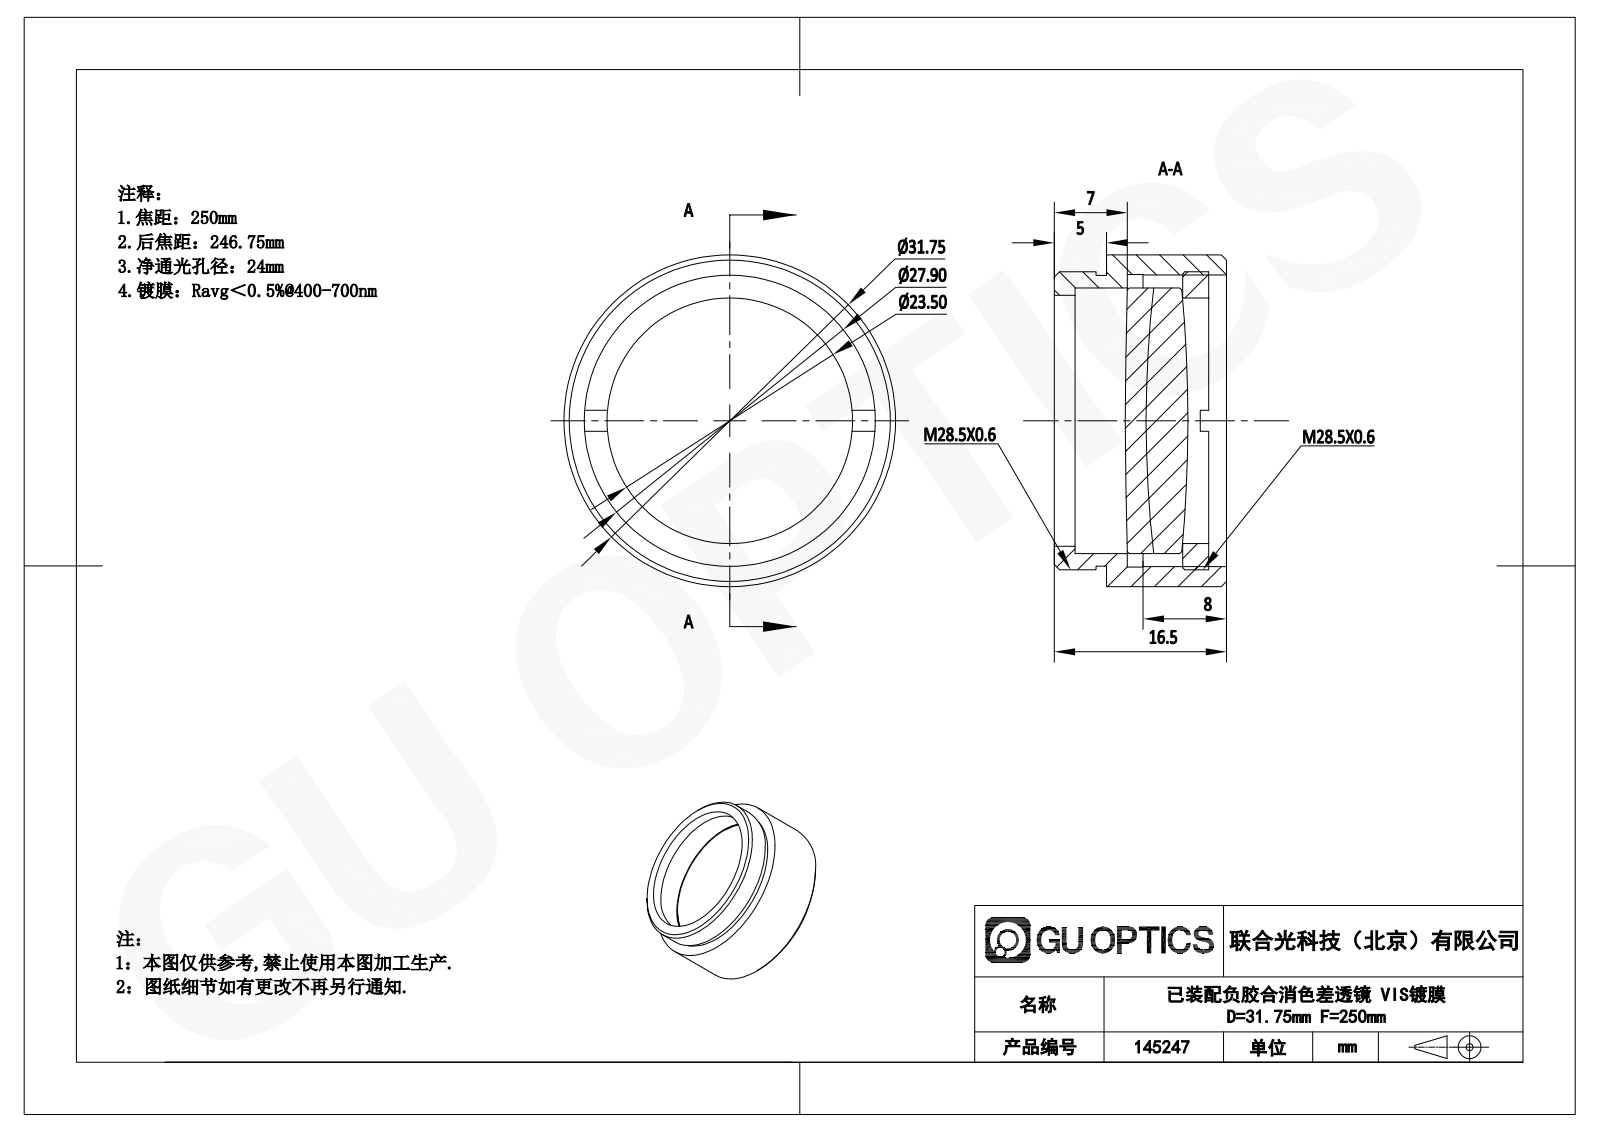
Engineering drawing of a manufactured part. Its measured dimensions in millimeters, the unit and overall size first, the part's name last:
Units: millimetres
Overall size (bounding box): 31.76 × 31.76 × 16.5
Round holes (diameter × count): ⌀23.5 ×1, ⌀24 ×1, ⌀27.9 ×1, ⌀28 ×1
Round bosses / shafts (diameter × count): ⌀31.76 ×1, ⌀28.5 ×1, ⌀27.8 ×1, ⌀25.4 ×1
Main face-to-face distances: 2, 5, 2.5, 7.29, 9.79, 12.29, 14.79, 16.5, 11.5, 4.21
Volume: 6 323 mm³ · Surface area: 6 907 mm²
Bodies: 4 solids, 56 faces (16 planar, 22 cylindrical, 18 other)
Part name (STEP PRODUCT): GL31-025B-250-VIS_Solidworks; M28.5x0.6ѹȦ; APD-ML25-250-VIS
STEP written by: SolidWorks 2022 (AUTOMOTIVE_DESIGN)
